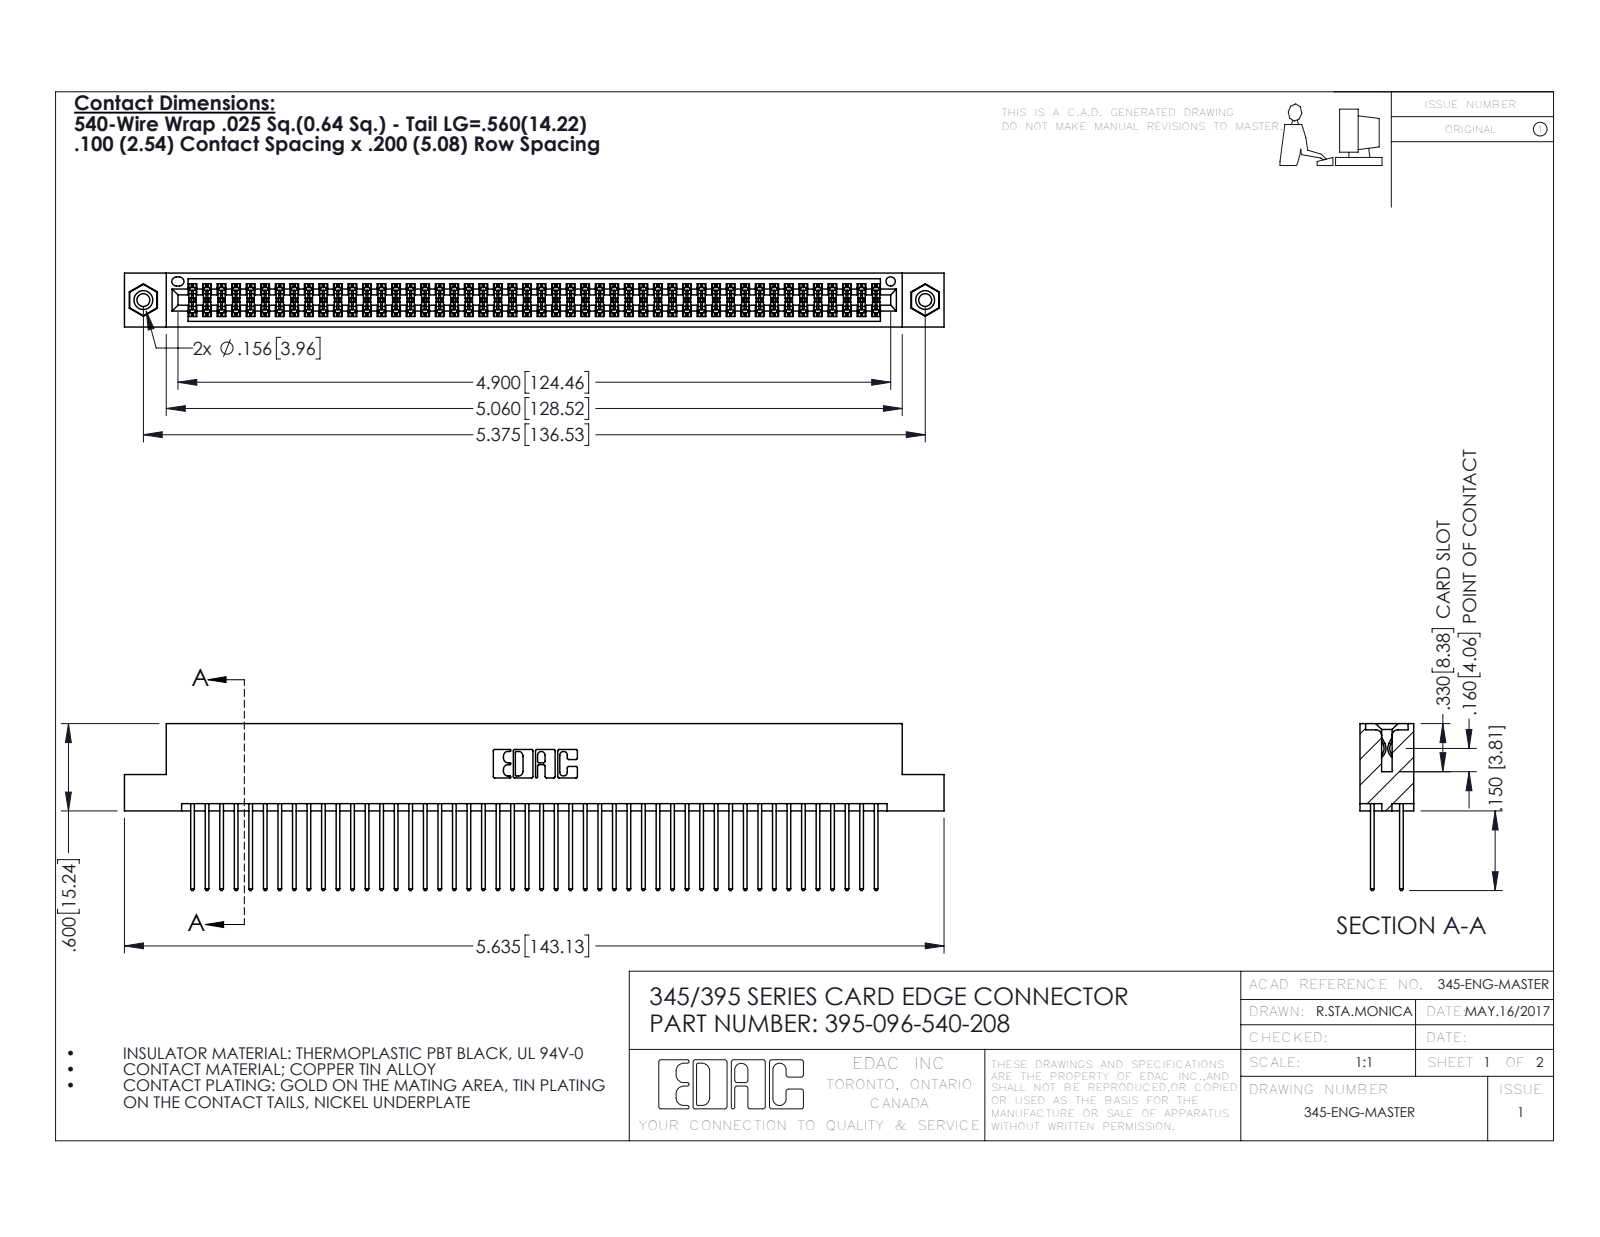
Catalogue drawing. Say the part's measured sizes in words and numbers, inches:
The part is named "345 Part_Flush Mounting Lugs - 0.156 Dia-TI; 345-292-001_345-293-140; 395-096-540-208; 345-250-001_345-250-003-102". Its 3-D file was written by "SolidWorks 2016 (CONFIG_CONTROL_DESIGN)". It is 99 solids with 4986 faces: 3280 planar, 1690 cylindrical and 16 other. Overall it measures 5.635 by 1.147 by 0.37 inches. Its volume is 0.874 cubic inches and its surface area 35.62 square inches. Round holes: 2 of diameter 0.089, 2 of diameter 0.125, 2 of diameter 0.156, 1 of diameter 0.064. Round bosses or shafts: 2 of diameter 0.155. Partial cylindrical surfaces (rounded edges, fillets, slot ends): 144 of radius 0.006, 96 of radius 0.01, 22 of radius 0.01, 6 of radius 0.007, 6 of radius 0.031, 3 of radius 0.026, 2 of radius 0.014, 2 of radius 0.019. The main face-to-face distances are 0.072, 0.298, 0.2, 0.098, 0.272, 0.025, 0.37, 0.225, 0.175, 0.149. The hole center spacings are 0.27, 5.139, 5.375.
